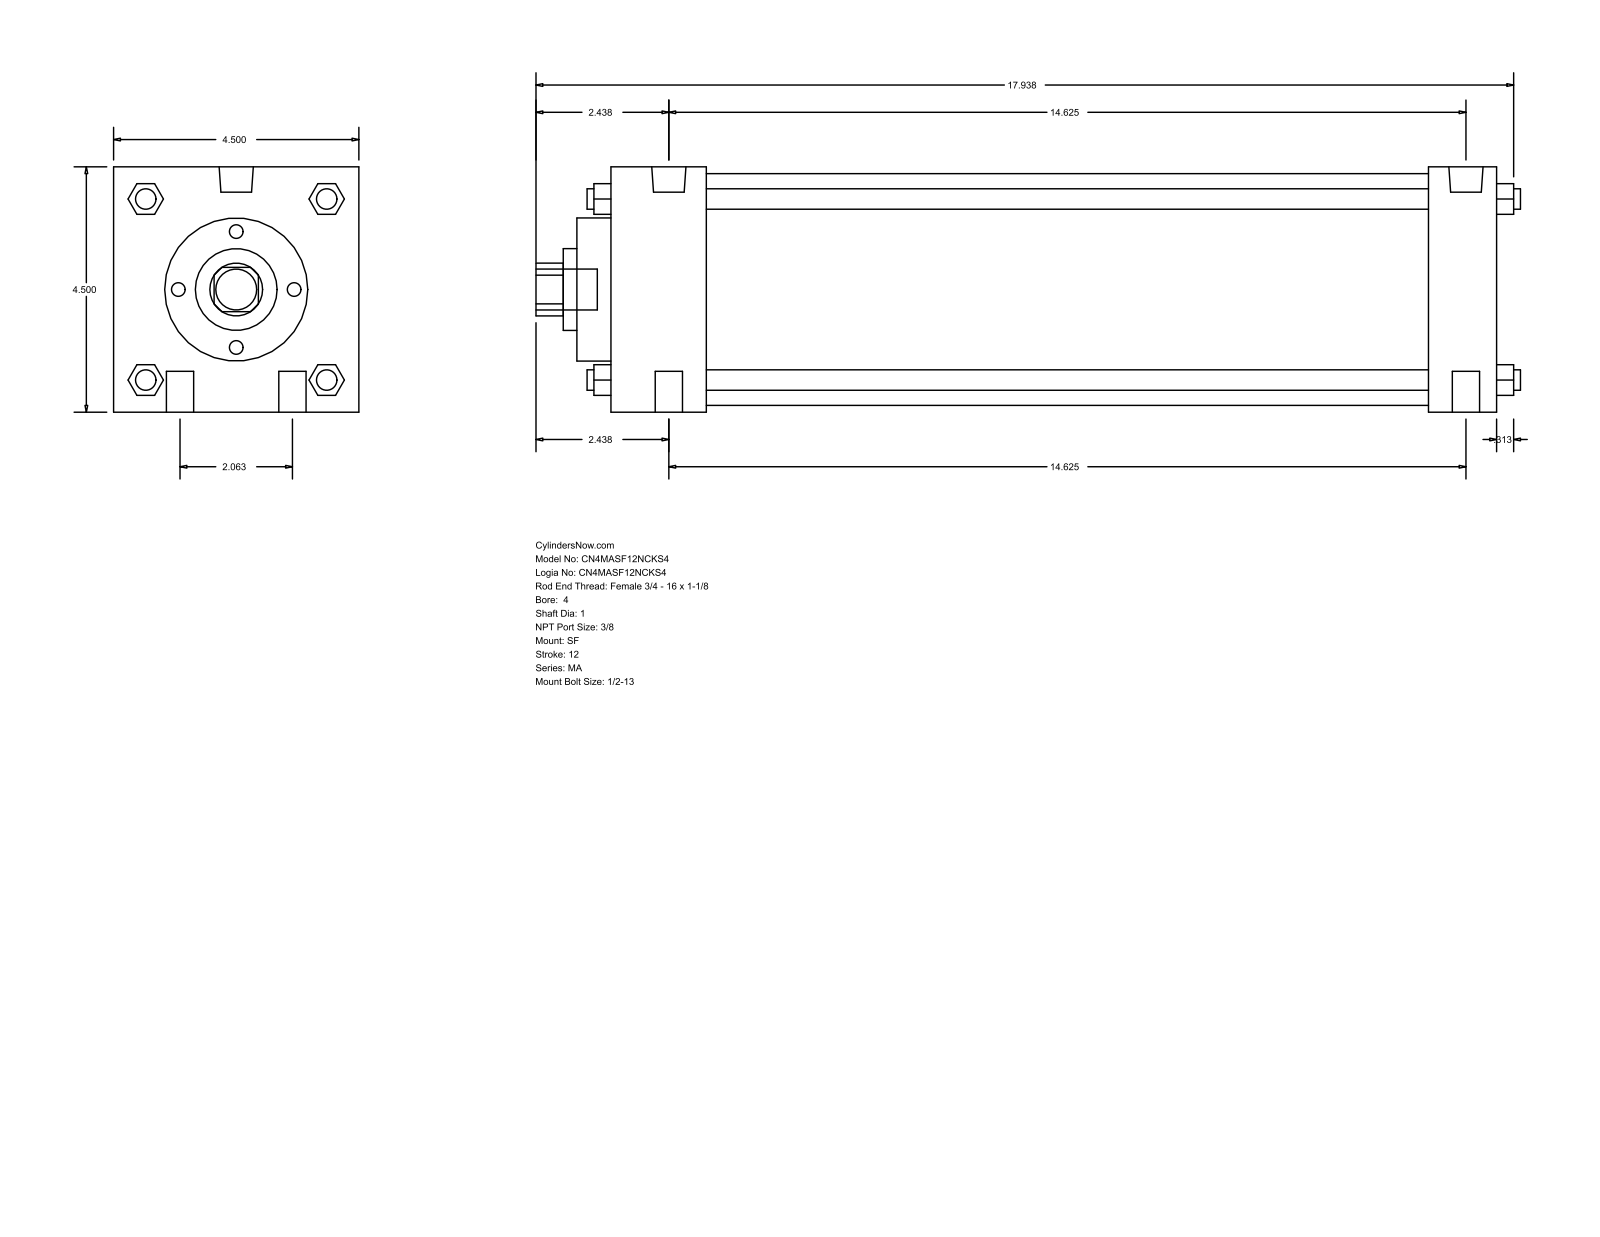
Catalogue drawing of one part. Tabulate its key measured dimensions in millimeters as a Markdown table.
| quantity | value |
| --- | --- |
| part name | MA_SF__0400_1 |
| STEP written by | GSSL Pune (CONFIG_CONTROL_DESIGN) |
| units | millimeters |
| bodies | 0 solids, 126 faces (95 planar, 31 cylindrical, 0 other) |
| overall size | 458.79 × 114.3 × 114.3 |
| round holes (diameter × count) | 25.4 × 1, 38.1 × 1, 66.67 × 1, 107.95 × 1 |
| round bosses / shafts (diameter × count) | 12.7 × 4, 9.53 × 4, 15.93 × 2, 11.11 × 2, 19.05 × 1 |
| partial cylindrical surfaces (radius × count) | 12.29 × 1 |
| main face-to-face distances | 114.3, 412.76, 381.01, 31.75, 44.46, 336.55, 368.3, 15.87, 60.33, 396.88 |
